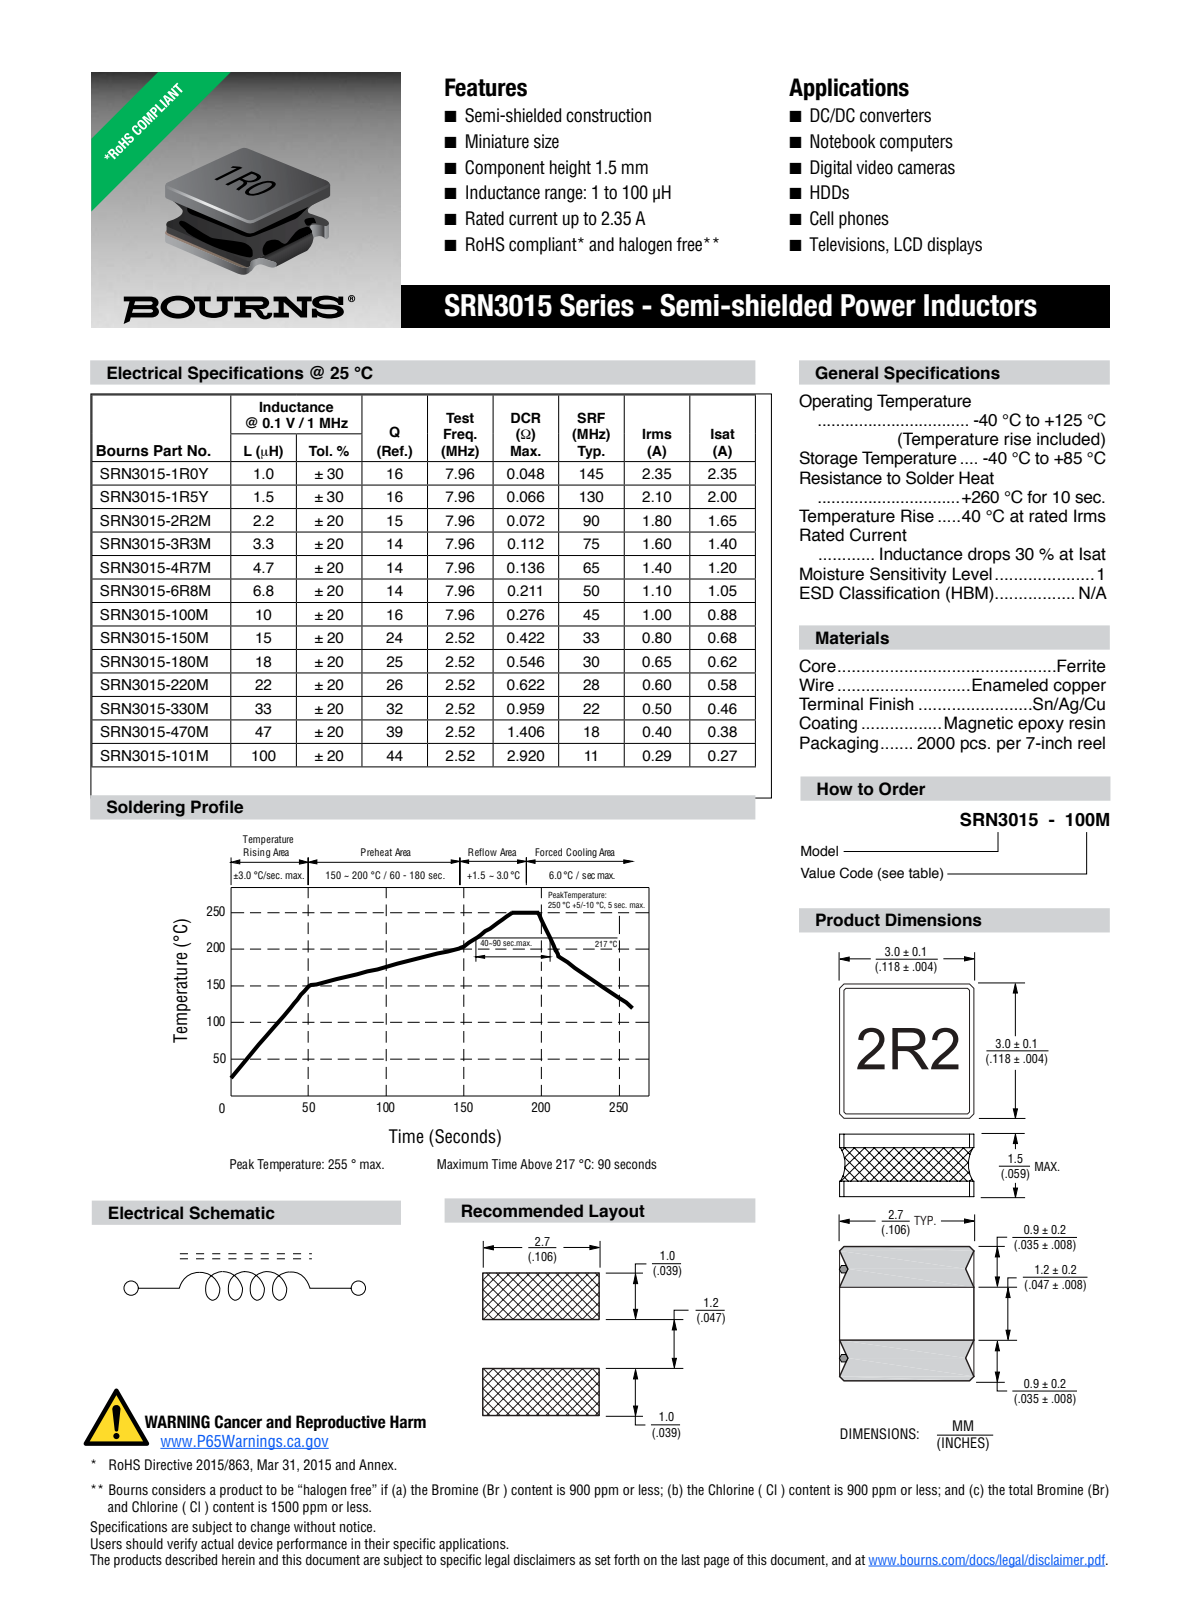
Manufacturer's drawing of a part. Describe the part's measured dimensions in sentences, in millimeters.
The part is named "SRN3015". Its 3-D file was written by "PRO/ENGINEER BY PARAMETRIC TECHNOLOGY CORPORATION, 2010100 (CONFIG_CONTROL_DESIGN)". It is 1 solid with 76 faces: 36 planar, 24 cylindrical and 16 other. Overall it measures 3 by 3 by 1.5 millimeters. Its volume is 11 cubic millimeters and its surface area 37 square millimeters. Partial cylindrical surfaces (rounded edges, fillets, slot ends): 16 of radius 0.2. The main face-to-face distances are 1.5, 2.75, 2.5, 3, 1.25, 1, 3.74, 0.36, 4.1, 3.75.
